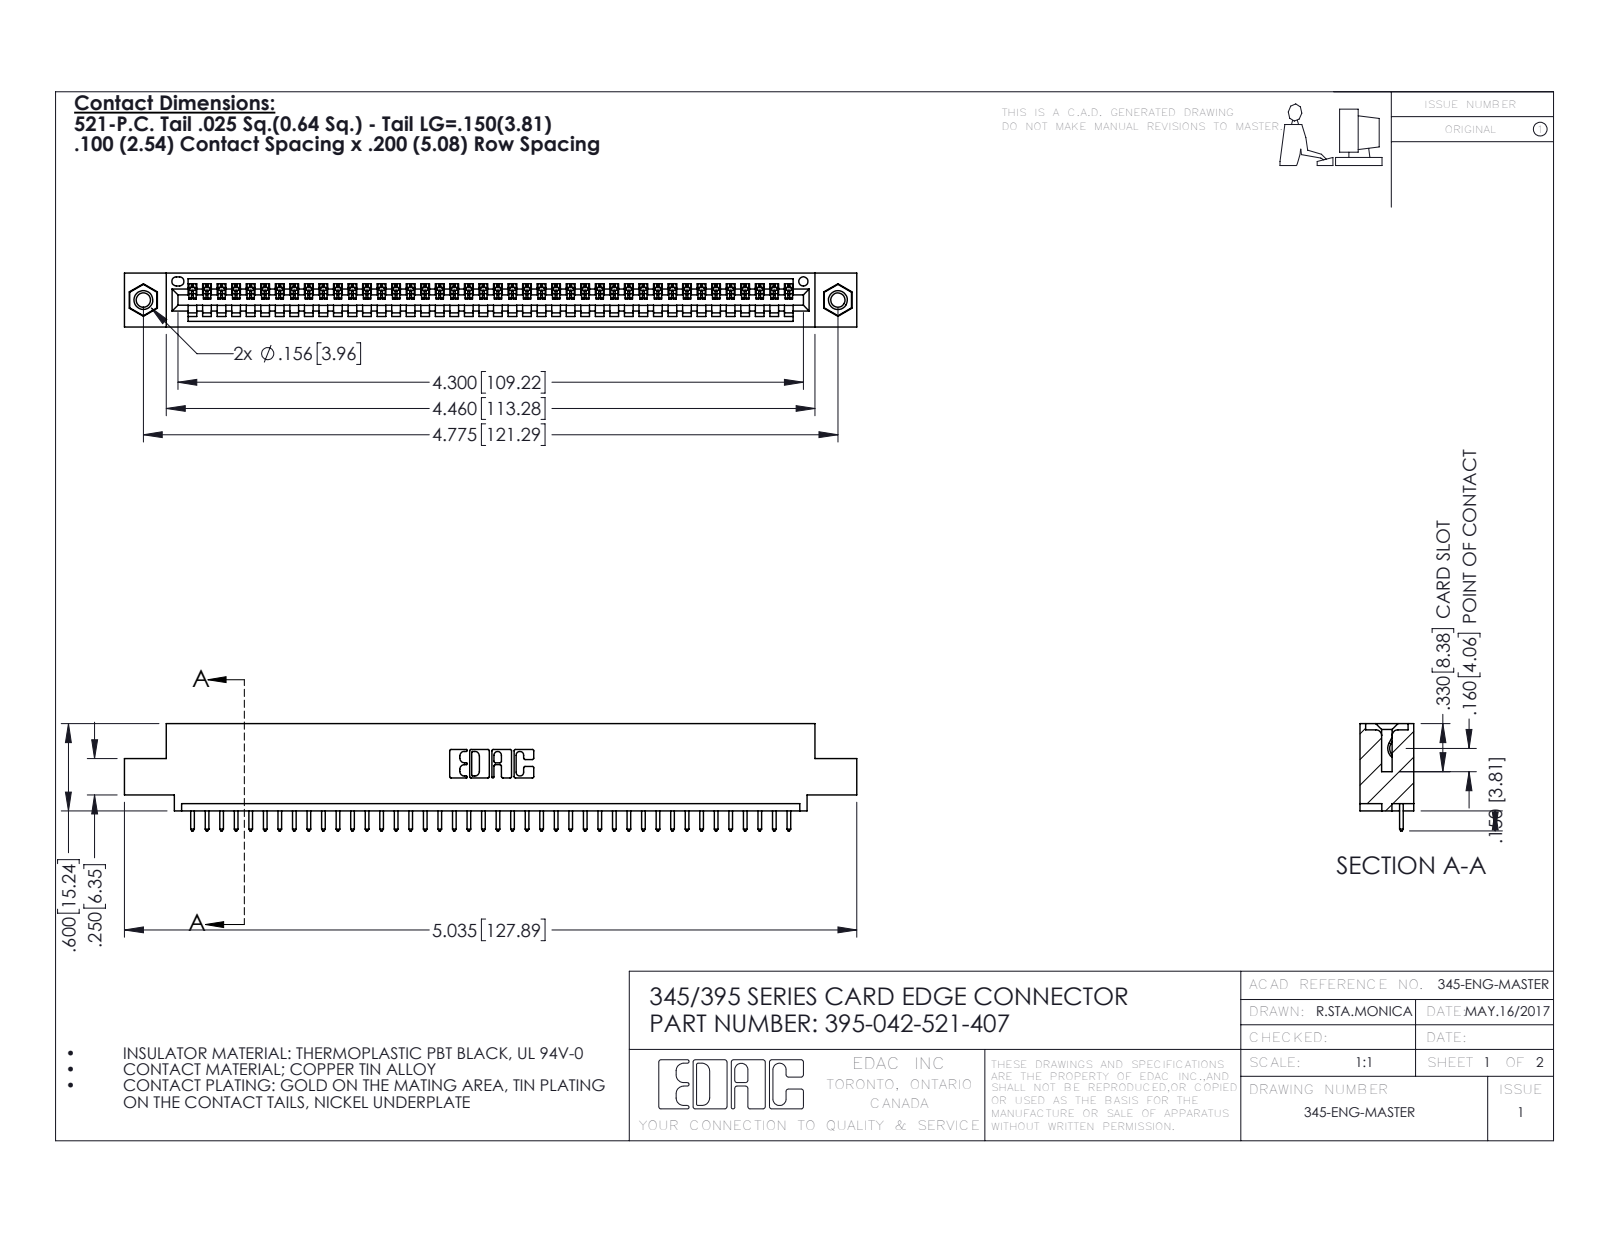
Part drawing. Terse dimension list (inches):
name: 345-250-001_345-250-005-103; 345 Part_0.110 Offset - 0.156 Dia-TI; 395-042-521-407; 345-292-001_345-293-121
written by: SolidWorks 2016 (CONFIG_CONTROL_DESIGN)
unit: in
bodies: 45 solids, 2626 faces (1796 planar, 814 cylindrical, 16 other)
size: 5.035 × 0.737 × 0.37
volume: 0.729 in³; area: 24.05 in²
holes: 2× ⌀0.098, 2× ⌀0.125, 2× ⌀0.156, 1× ⌀0.064
bosses: 2× ⌀0.155
rounds: 84× R0.006, 84× R0.01, 22× R0.01, 6× R0.007, 6× R0.031, 3× R0.026, 2× R0.031, 2× R0.04
face distances: 0.072, 0.298, 0.37, 0.2, 0.098, 0.272, 0.025, 0.225, 0.149, 0.072
hole spacings: 0.27, 4.539, 4.775
